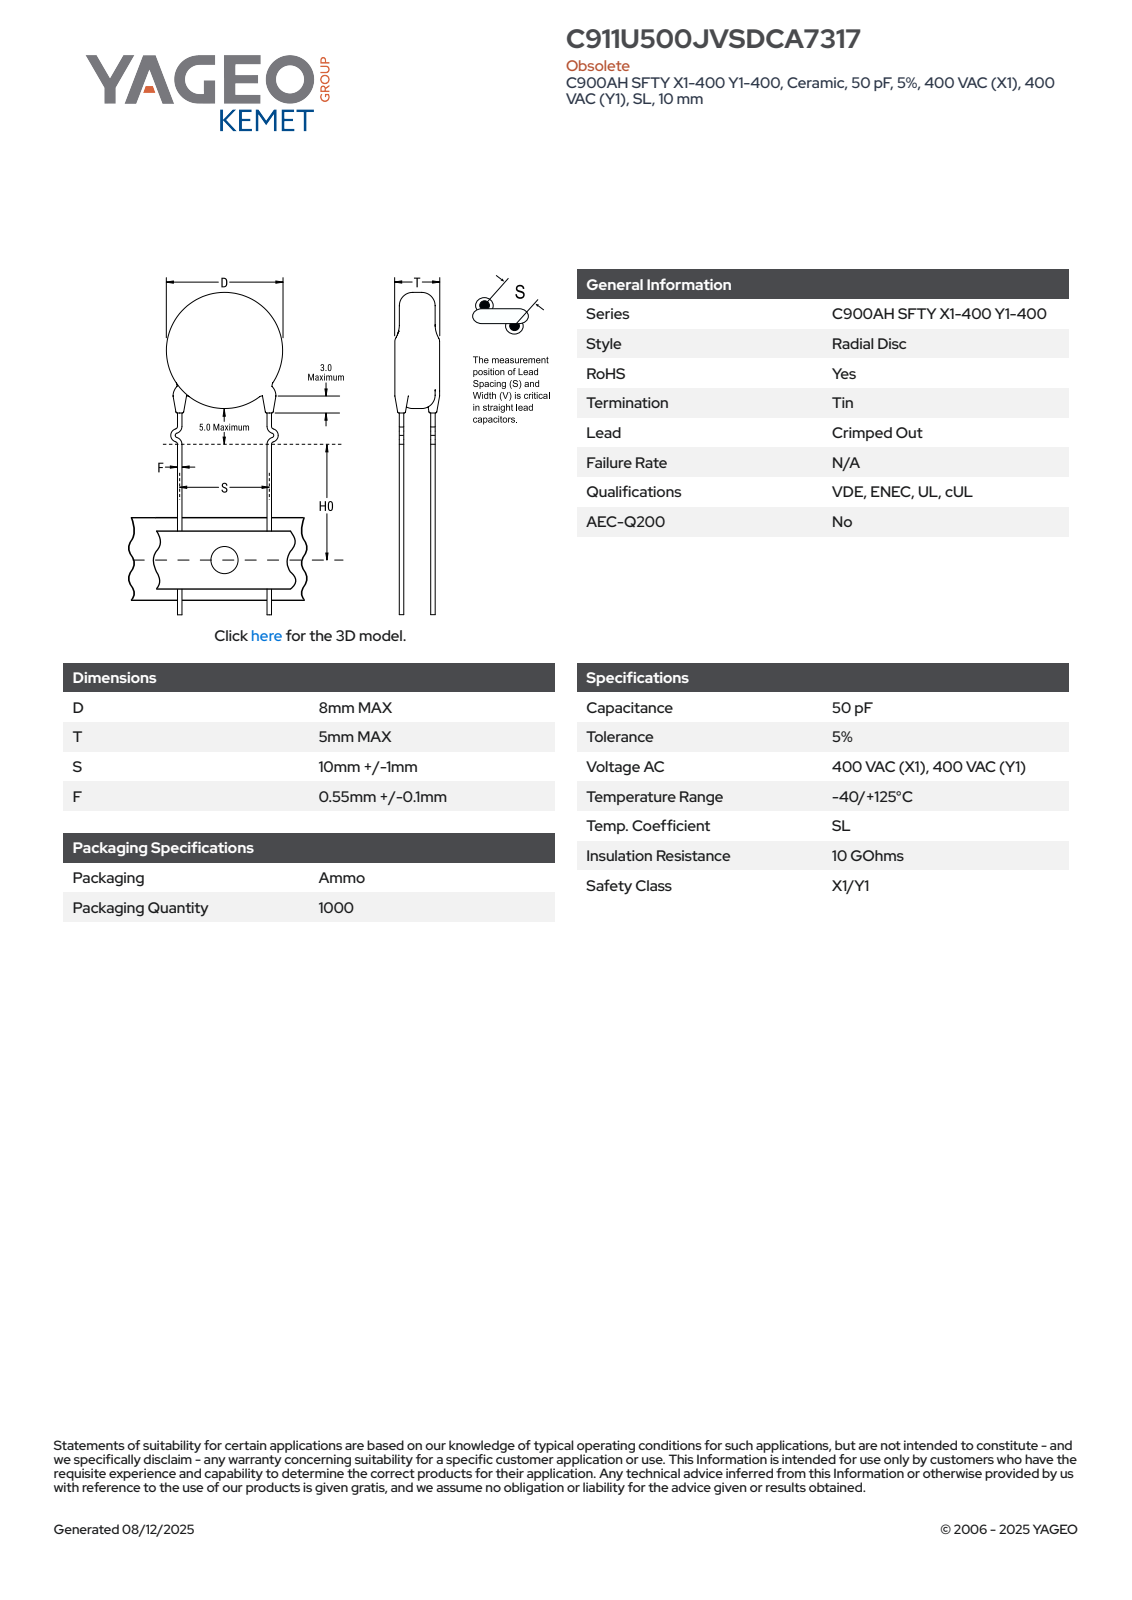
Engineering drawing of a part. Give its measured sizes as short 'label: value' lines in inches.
name: CCD_KCOC900_D8T5S10LL20F0.55
written by: SolidWorks 2014 (AUTOMOTIVE_DESIGN)
unit: in
bodies: 4 solids, 93 faces (63 planar, 10 cylindrical, 20 other)
size: 1.299 × 0.561 × 0.249
volume: 0.016 in³; area: 0.535 in²
bosses: 4× ⌀0.047, 1× ⌀0.315
face distances: 0.197, 0.033, 0.174, 0.141, 0.133, 0.02, 0.012, 0.026, 0.067, 0.097
